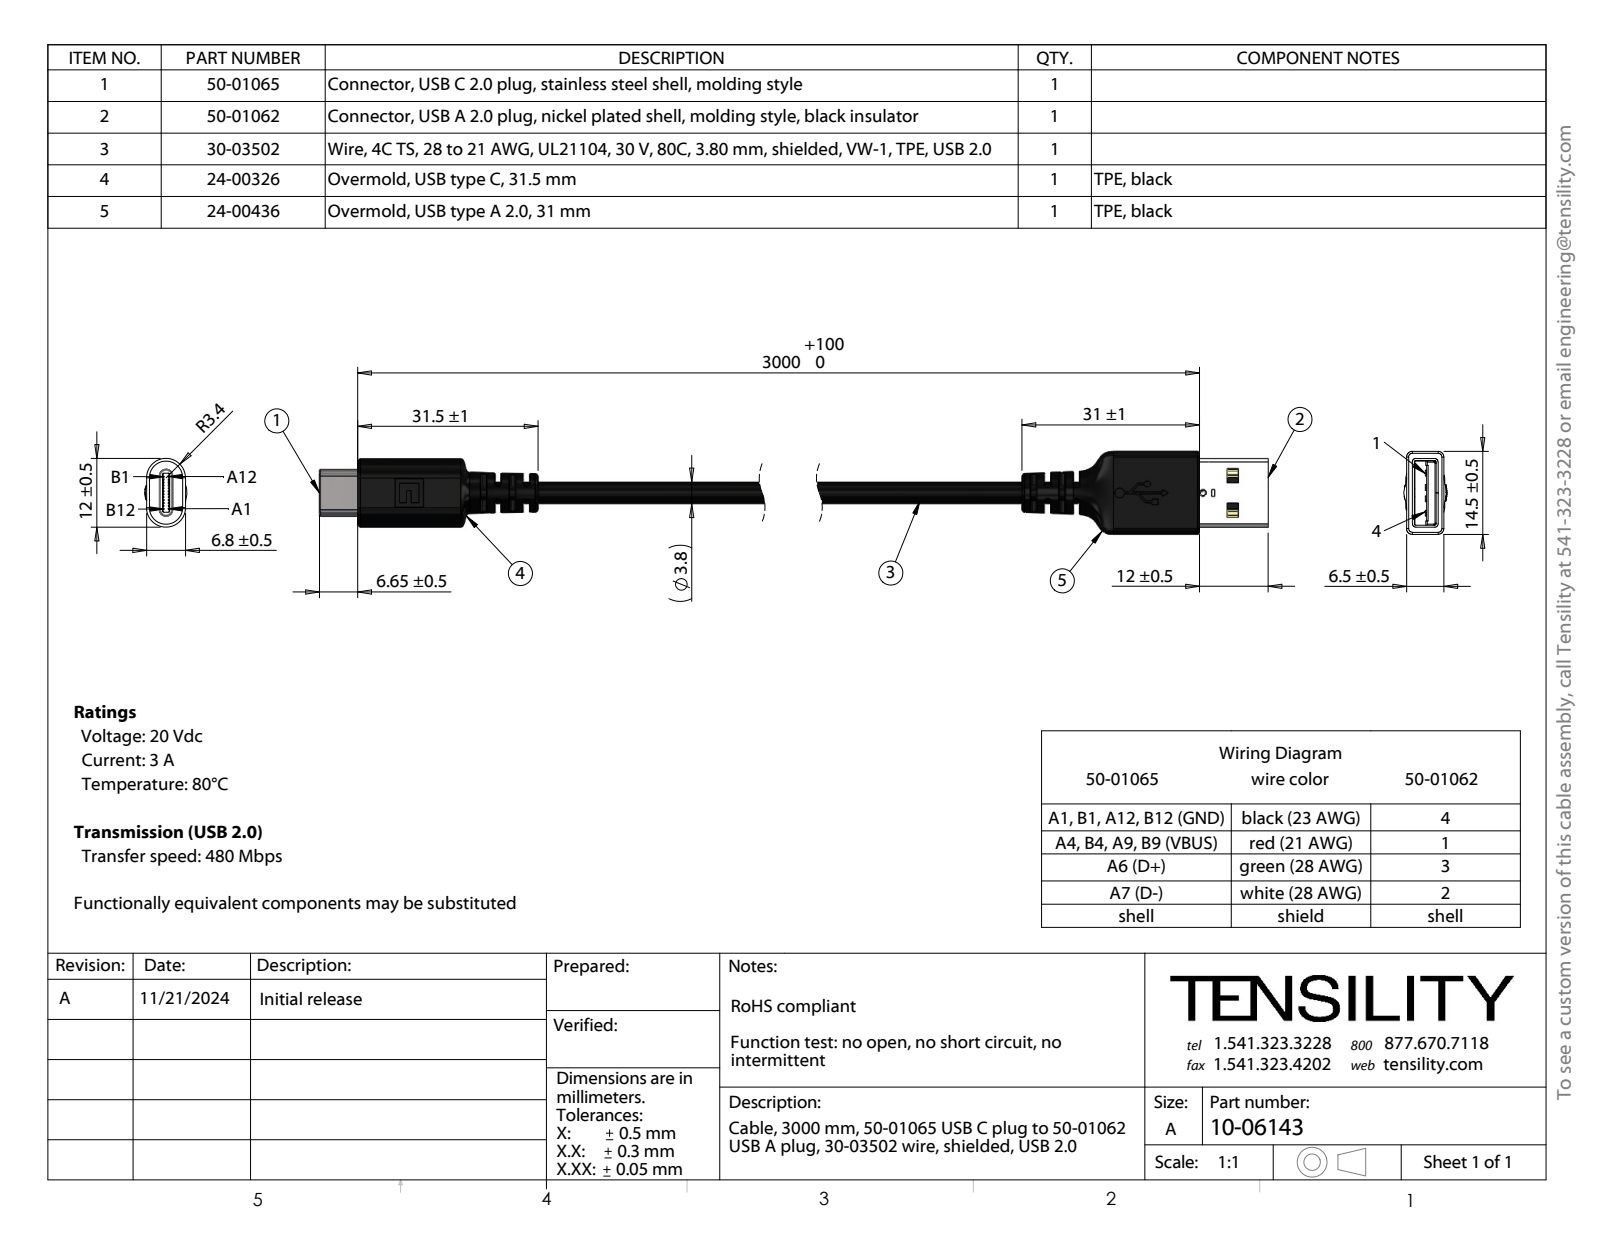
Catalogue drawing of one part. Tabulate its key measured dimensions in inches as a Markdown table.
| quantity | value |
| --- | --- |
| part name | 24-00436; 50-01062_pin3; 50-01062_Assembled; 50-01062_shell2 (+8 more) |
| STEP written by | SolidWorks 2021 (CONFIG_CONTROL_DESIGN) |
| units | inches |
| bodies | 125 solids, 1970 faces (1014 planar, 630 cylindrical, 326 other) |
| overall size | 7.88 × 0.571 × 0.297 |
| volume | 0.361 in³ |
| surface area | 35 in² |
| round holes (diameter × count) | 0.041 × 1, 0.069 × 1, 0.103 × 1, 0.104 × 1, 0.112 × 1 |
| round bosses / shafts (diameter × count) | 0.033 × 2, 0.15 × 1, 0.104 × 1, 0.047 × 1, 0.039 × 1 |
| partial cylindrical surfaces (radius × count) | 0.01 × 40, 0.008 × 34, 0.02 × 32, 0.014 × 14, 0.016 × 14, 0.012 × 13, 0.012 × 5, 0.024 × 5 |
| main face-to-face distances | 0.014, 0.163, 0.039, 0.217, 0.053, 0.203, 0.059, 0.098, 0.177, 0.15 |
| hole center spacings | 0.202 |
